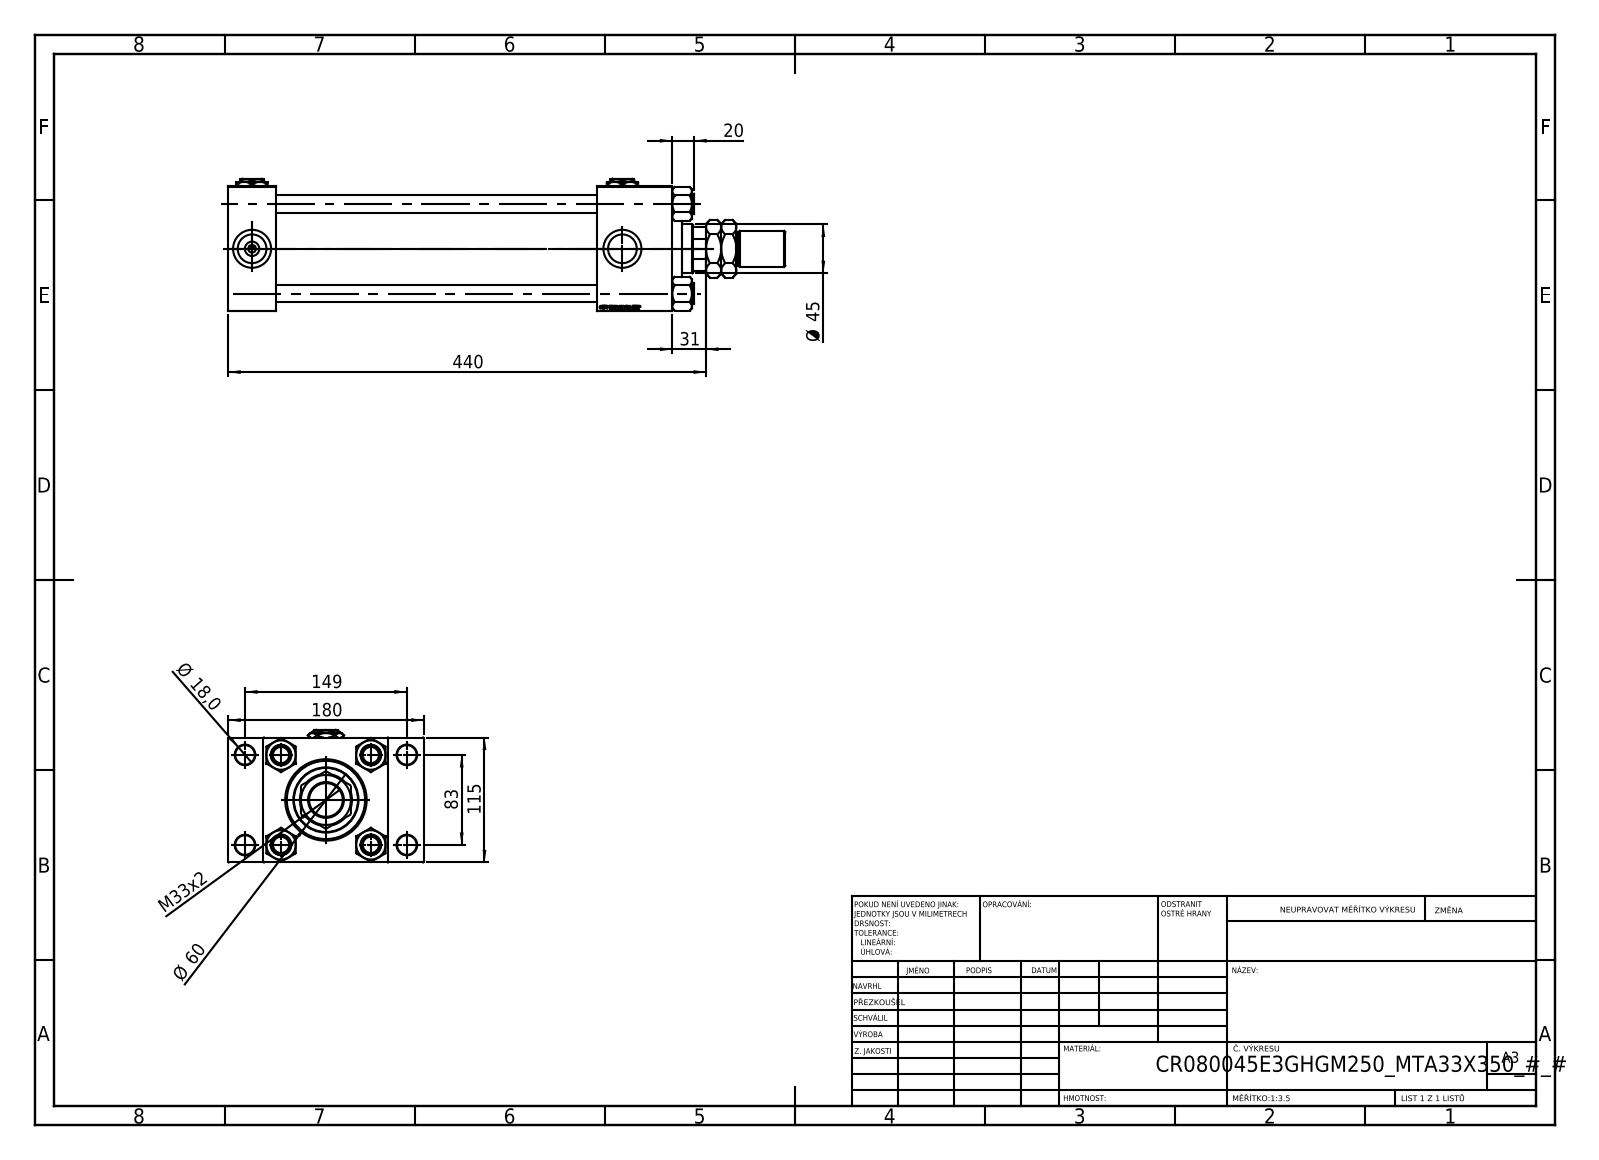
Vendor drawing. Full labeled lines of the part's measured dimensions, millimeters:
Part name (STEP PRODUCT): Zatka_pro_OIL_PORT; V215_VC_A; V215CR_E_Body; V215CR_VCP_E (+3 more)
STEP written by: SolidWorks 2019 (CONFIG_CONTROL_DESIGN)
Units: millimetres
Bodies: 14 solids, 1333 faces (608 planar, 101 cylindrical, 624 other)
Overall size (bounding box): 513 × 180 × 122
Volume: 2 922 000 mm³ · Surface area: 534 128 mm²
Round holes (diameter × count): ⌀16 ×4, ⌀18 ×4, ⌀26.44 ×4, ⌀35 ×4, ⌀7 ×3, ⌀31.5 ×1, ⌀45 ×1, ⌀48 ×1, ⌀61 ×1, ⌀72 ×1, ⌀80 ×1
Round bosses / shafts (diameter × count): ⌀19 ×4, ⌀86 ×1, ⌀60 ×1, ⌀33 ×1, ⌀31 ×1
Partial cylindrical surfaces — rounded edges, fillets, slot ends (radius × count): R22 ×1
Main face-to-face distances: 115, 44, 409, 365, 32.5, 147.5, 69, 340, 296, 46
Hole centre spacings: 33.15, 58.48, 82.7, 85.28, 89.24, 115.85, 142.43, 83
